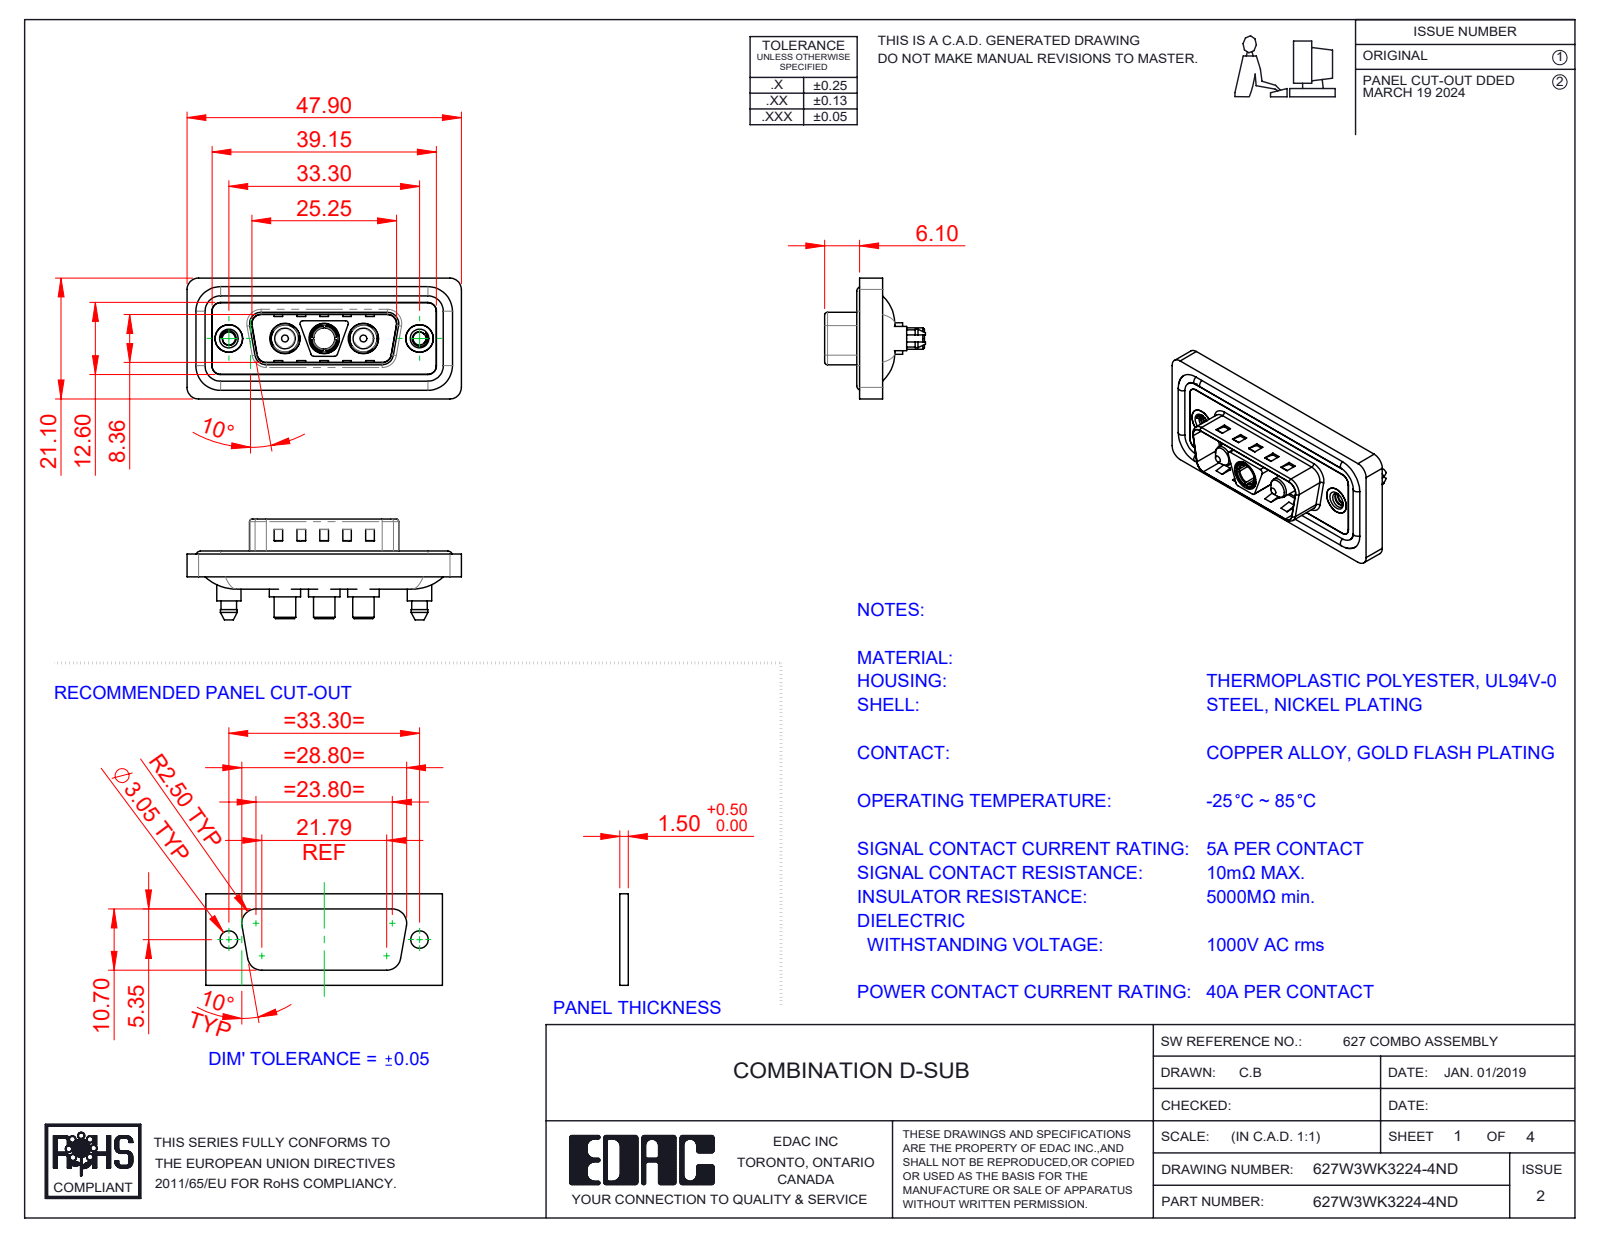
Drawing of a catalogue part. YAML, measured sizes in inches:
part_name: "627Combo Shell Rear_15 Contacts; 627Combo Threaded Boardlock_D; 627Combo Waterproof Housing_15 Contacts; 627W3WK3224-4ND (+5 more)"
step_written_by: "SolidWorks 2023 (CONFIG_CONTROL_DESIGN)"
units: inches
bodies: {solids: 13, faces: 667, planar: 247, cylindrical: 290, other: 130}
overall_size: [1.886, 0.831, 0.693]
volume: 0.359
surface_area: 14.72
round_holes:
  - {diameter: 0.191, count: 3}
  - {diameter: 0.209, count: 3}
  - {diameter: 0.089, count: 2}
  - {diameter: 0.157, count: 2}
  - {diameter: 0.189, count: 2}
  - {diameter: 0.197, count: 2}
  - {diameter: 0.146, count: 1}
round_bosses_or_shafts:
  - {diameter: 0.063, count: 4}
  - {diameter: 0.217, count: 3}
  - {diameter: 0.205, count: 3}
  - {diameter: 0.187, count: 3}
  - {diameter: 0.148, count: 3}
  - {diameter: 0.213, count: 2}
  - {diameter: 0.193, count: 2}
  - {diameter: 0.167, count: 2}
partial_cylinders:
  - {radius: 0.059, count: 28}
  - {radius: 0.079, count: 20}
  - {radius: 0.02, count: 12}
  - {radius: 0.063, count: 10}
  - {radius: 0.01, count: 4}
  - {radius: 0.024, count: 4}
  - {radius: 0.026, count: 4}
  - {radius: 0.035, count: 4}
face_to_face_distances: [0.016, 0.043, 0.059, 0.122, 0.02, 0.063, 0.114, 0.157, 0.028, 0.032]
hole_center_spacings: [0.27, 0.386, 0.656, 0.925, 0.539, 1.311]
